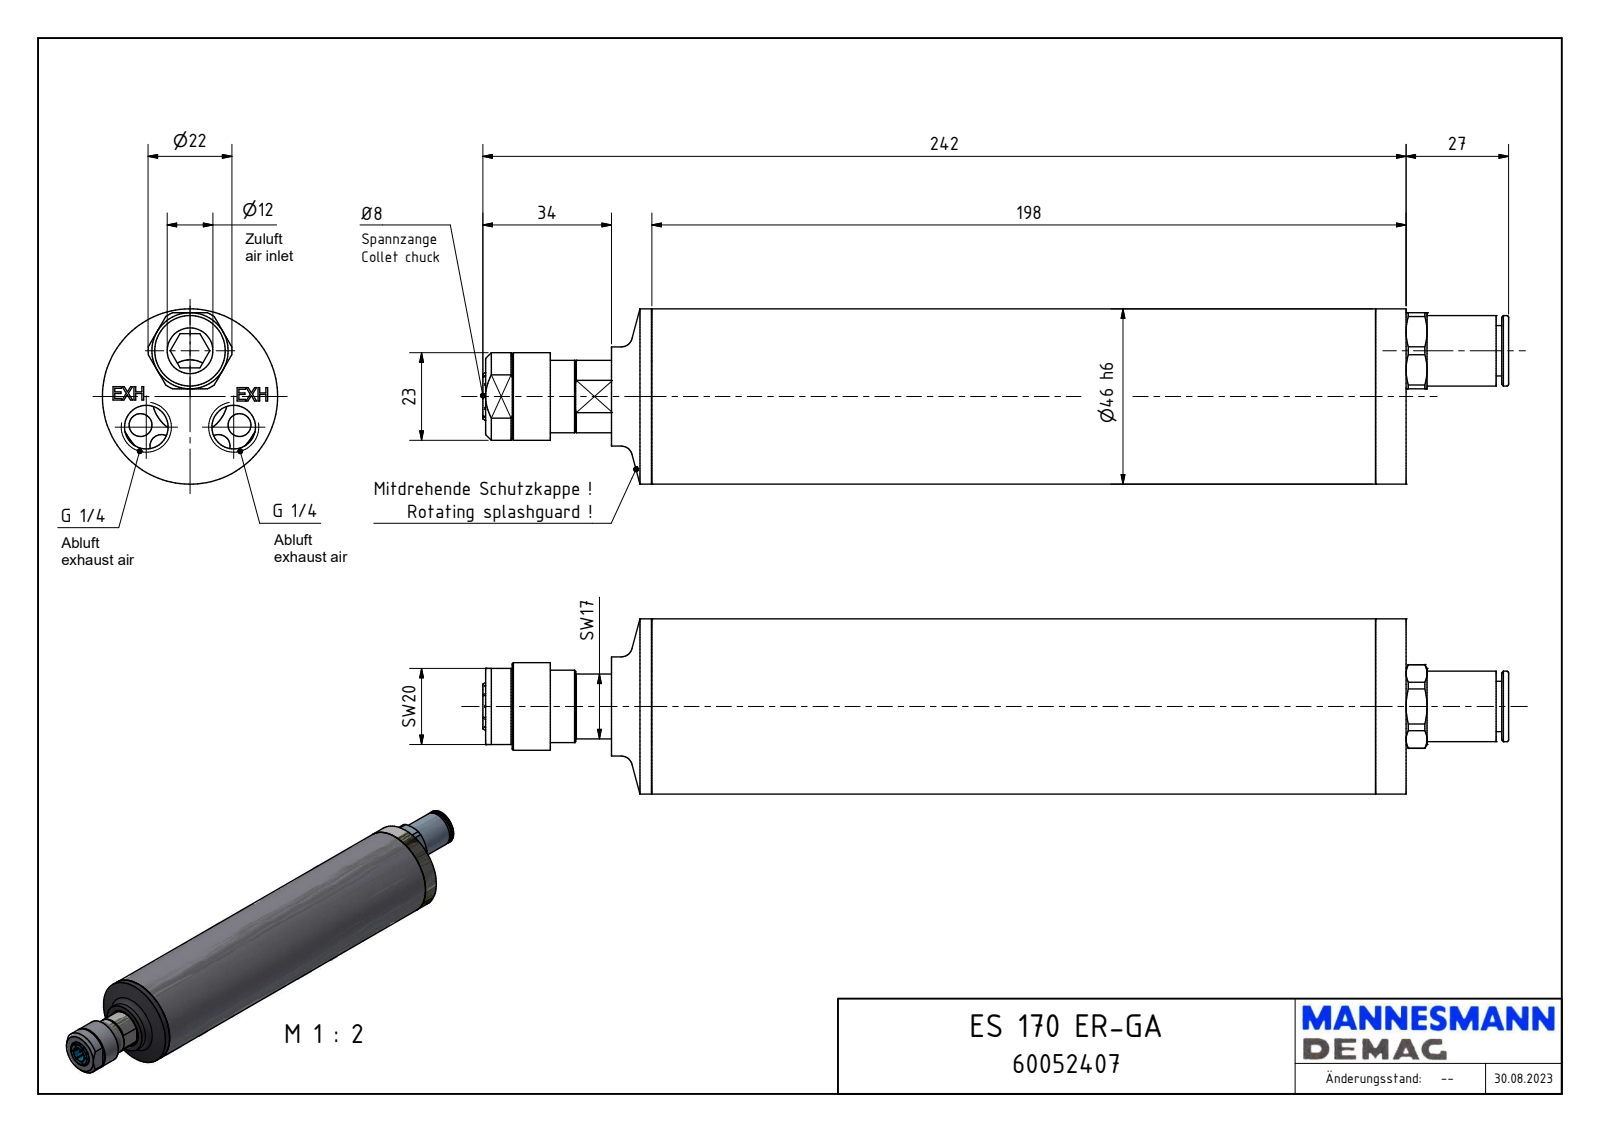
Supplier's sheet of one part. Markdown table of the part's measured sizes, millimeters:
| quantity | value |
| --- | --- |
| part name | ES 170 ER-GA_60052407 |
| STEP written by | Autodesk Inventor 2024 (AUTOMOTIVE_DESIGN) |
| units | millimeters |
| bodies | 1 solid, 233 faces (157 planar, 44 cylindrical, 32 other) |
| overall size | 269.27 × 46 × 46 |
| volume | 352 785 mm³ |
| surface area | 39 936 mm² |
| round holes (diameter × count) | 11.45 × 2, 8 × 1, 12 × 1, 13.2 × 1, 20.3 × 1 |
| round bosses / shafts (diameter × count) | 46 × 1, 44.6 × 1, 26 × 1, 23 × 1, 19 × 1, 18.5 × 1, 14 × 1, 13.2 × 1 |
| partial cylindrical surfaces (radius × count) | 33.72 × 6, 11 × 1 |
| main face-to-face distances | 3, 20, 17, 205.6, 208.6, 10.5, 33.04, 238.64, 241.64, 5.5 |
| hole center spacings | 14, 23.08, 12, 22.94 |
